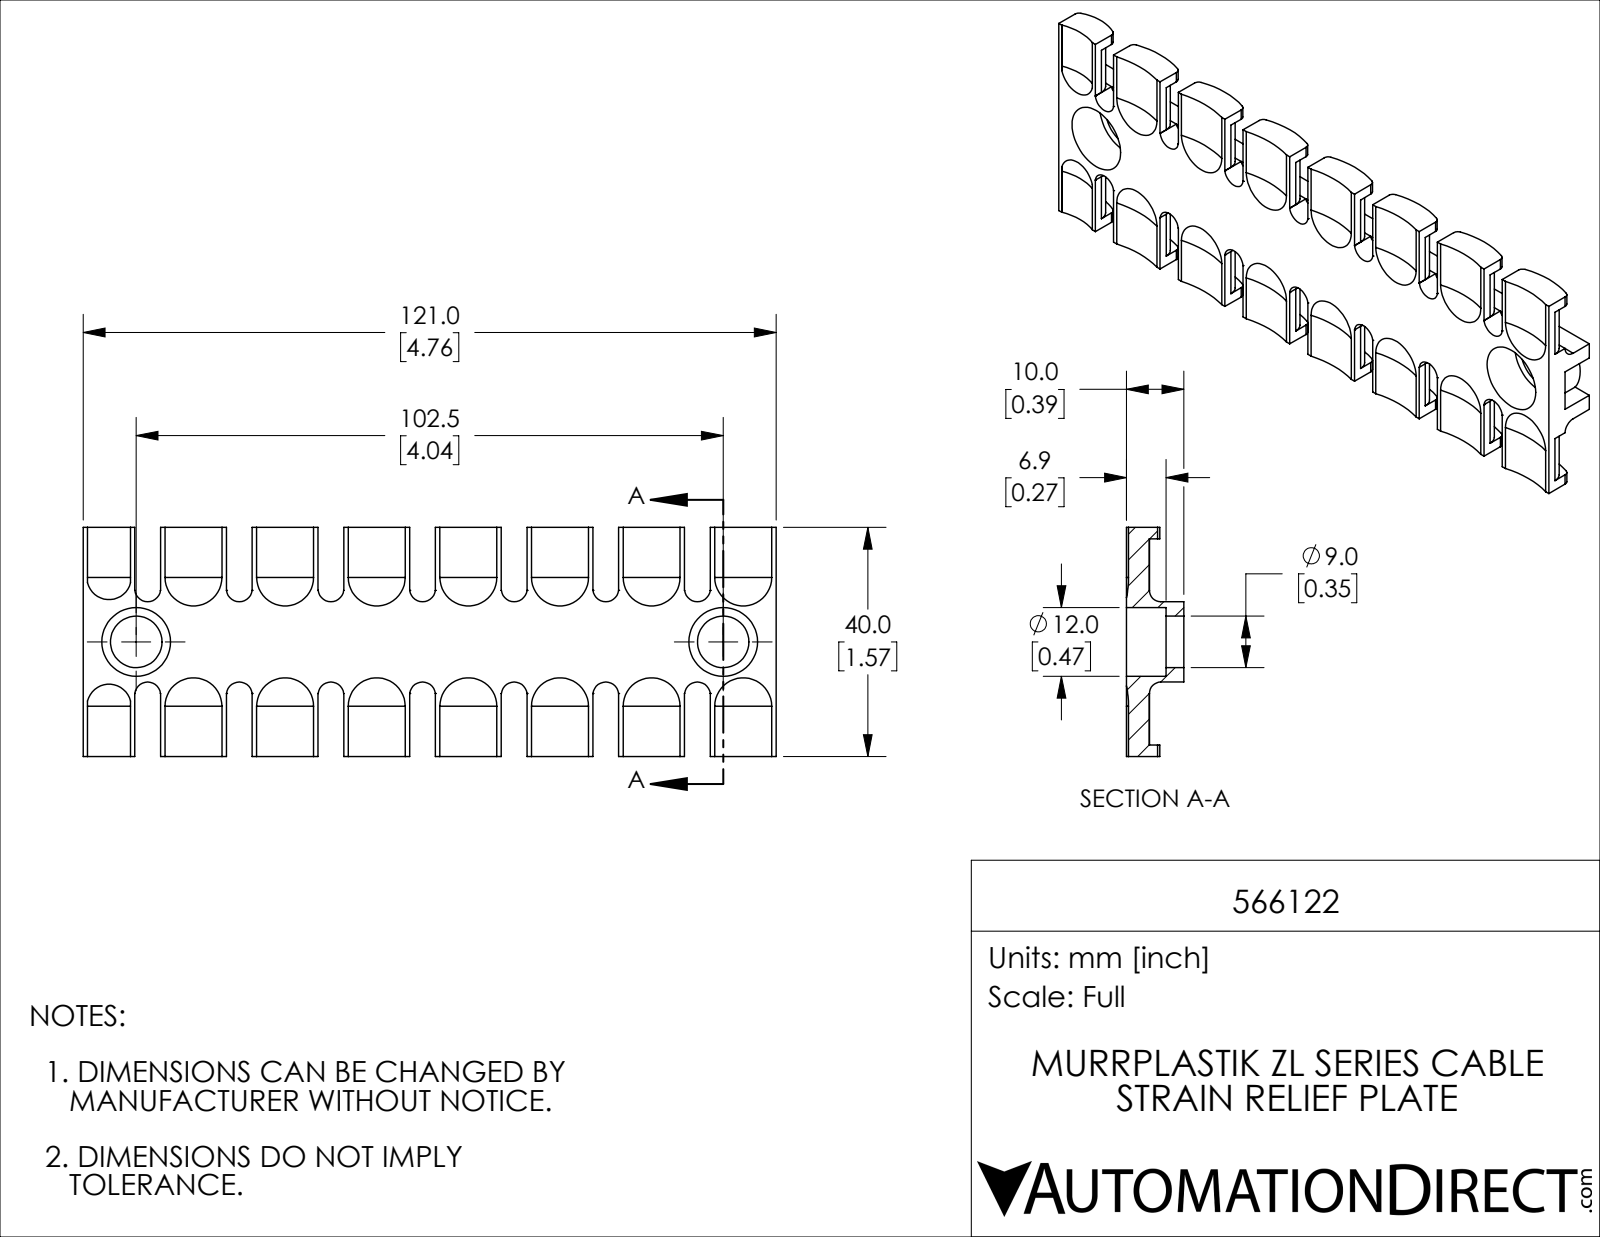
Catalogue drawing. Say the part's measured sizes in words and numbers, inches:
The part is named "566122". Its 3-D file was written by "SolidWorks 2019 (CONFIG_CONTROL_DESIGN)". It is 1 solid with 319 faces: 139 planar, 164 cylindrical and 16 other. Overall it measures 4.764 by 1.575 by 0.394 inches. Its volume is 1.192 cubic inches and its surface area 22.26 square inches. Round holes: 2 of diameter 0.354, 2 of diameter 0.472. Partial cylindrical surfaces (rounded edges, fillets, slot ends): 16 of radius 0.039, 16 of radius 0.098, 14 of radius 0.089, 7 of radius 0.63, 7 of radius 0.709, 2 of radius 0.079, 2 of radius 0.276, 1 of radius 0.354. The main face-to-face distances are 0.157, 0.63, 0.433, 0.118, 0.512, 1.063, 0.945, 0.236, 0.394, 0.551. The hole center spacings are 4.035.
